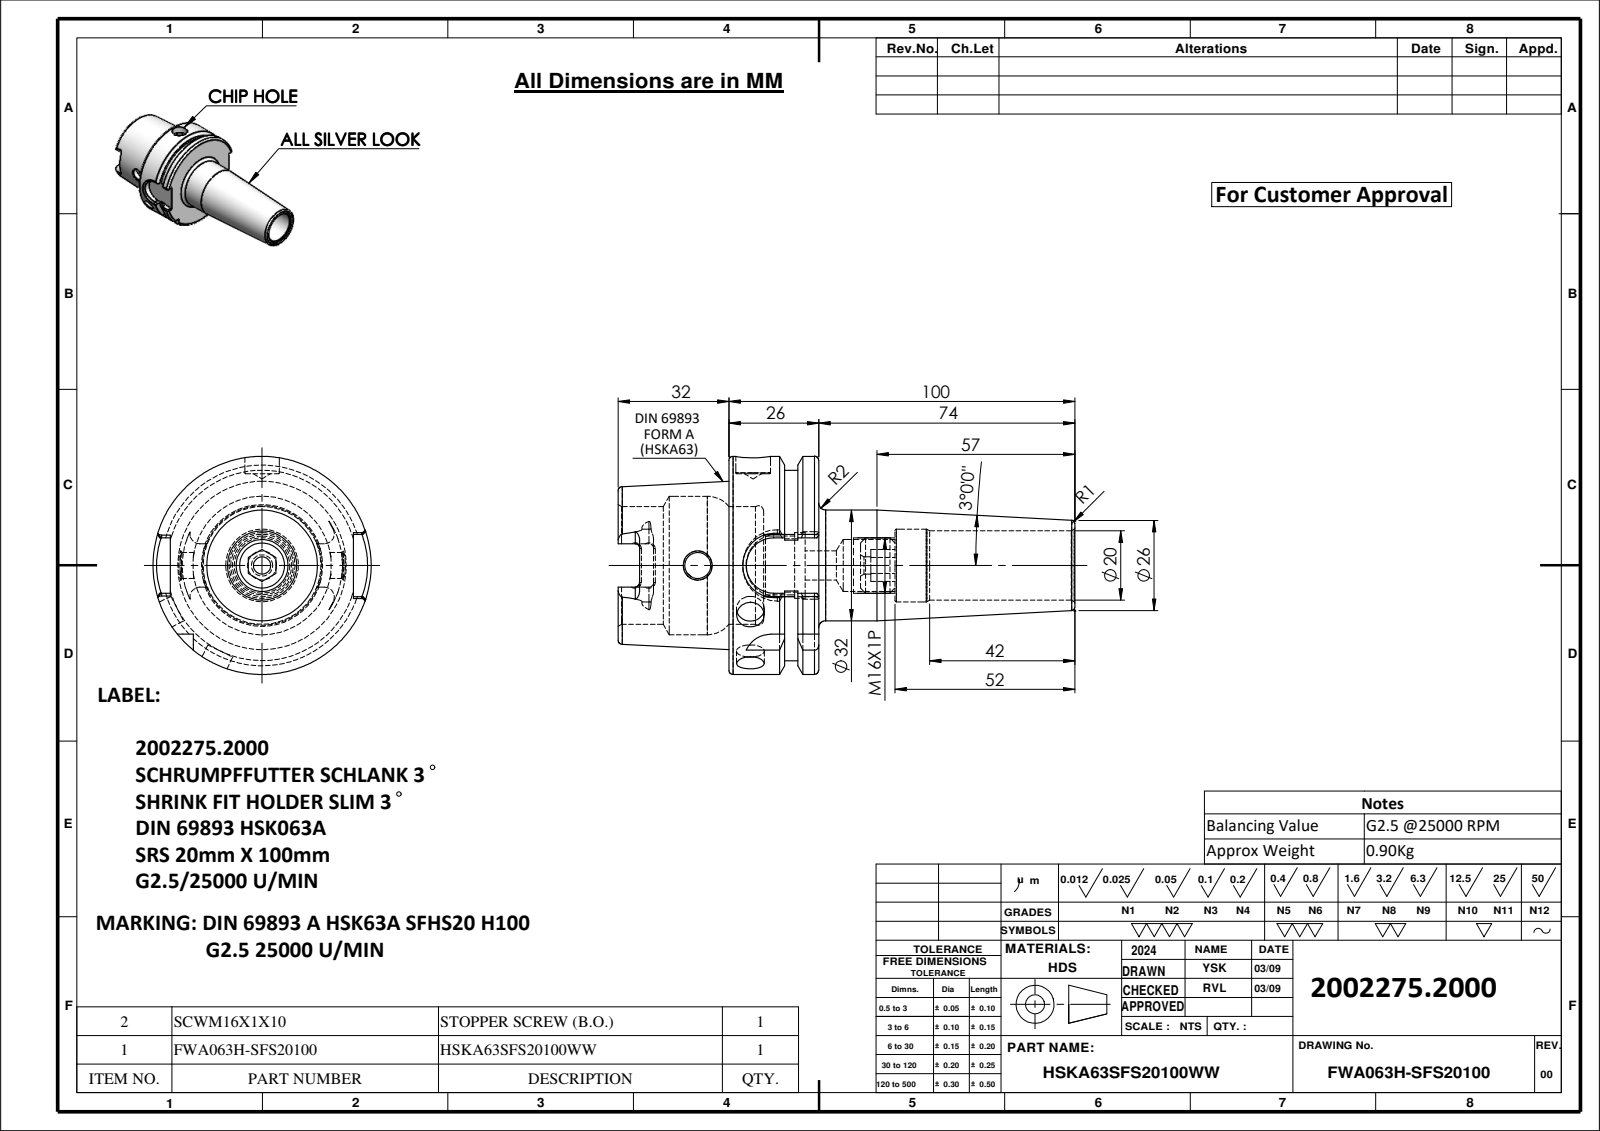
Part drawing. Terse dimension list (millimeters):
name: SCWM16X1X10; HSKA63SFS20100WW; FWA063H-SFS20100
written by: SolidWorks 2024 (CONFIG_CONTROL_DESIGN)
unit: mm
bodies: 2 solids, 196 faces (59 planar, 57 cylindrical, 80 other)
size: 132 × 63 × 63
volume: 113 983 mm³; area: 34 024 mm²
holes: 2× ⌀8, 1× ⌀5, 1× ⌀7.5, 1× ⌀8.4, 1× ⌀10, 1× ⌀15, 1× ⌀17, 1× ⌀19, 1× ⌀20, 1× ⌀21, 1× ⌀34, 1× ⌀40
bosses: 1× ⌀63, 1× ⌀55, 1× ⌀32, 1× ⌀16
rounds: 6× R1.3, 4× R2.88, 2× R8, 1× R9
face distances: 25.95, 10, 15.95, 32, 42, 57.95, 38, 52.9, 22, 54
